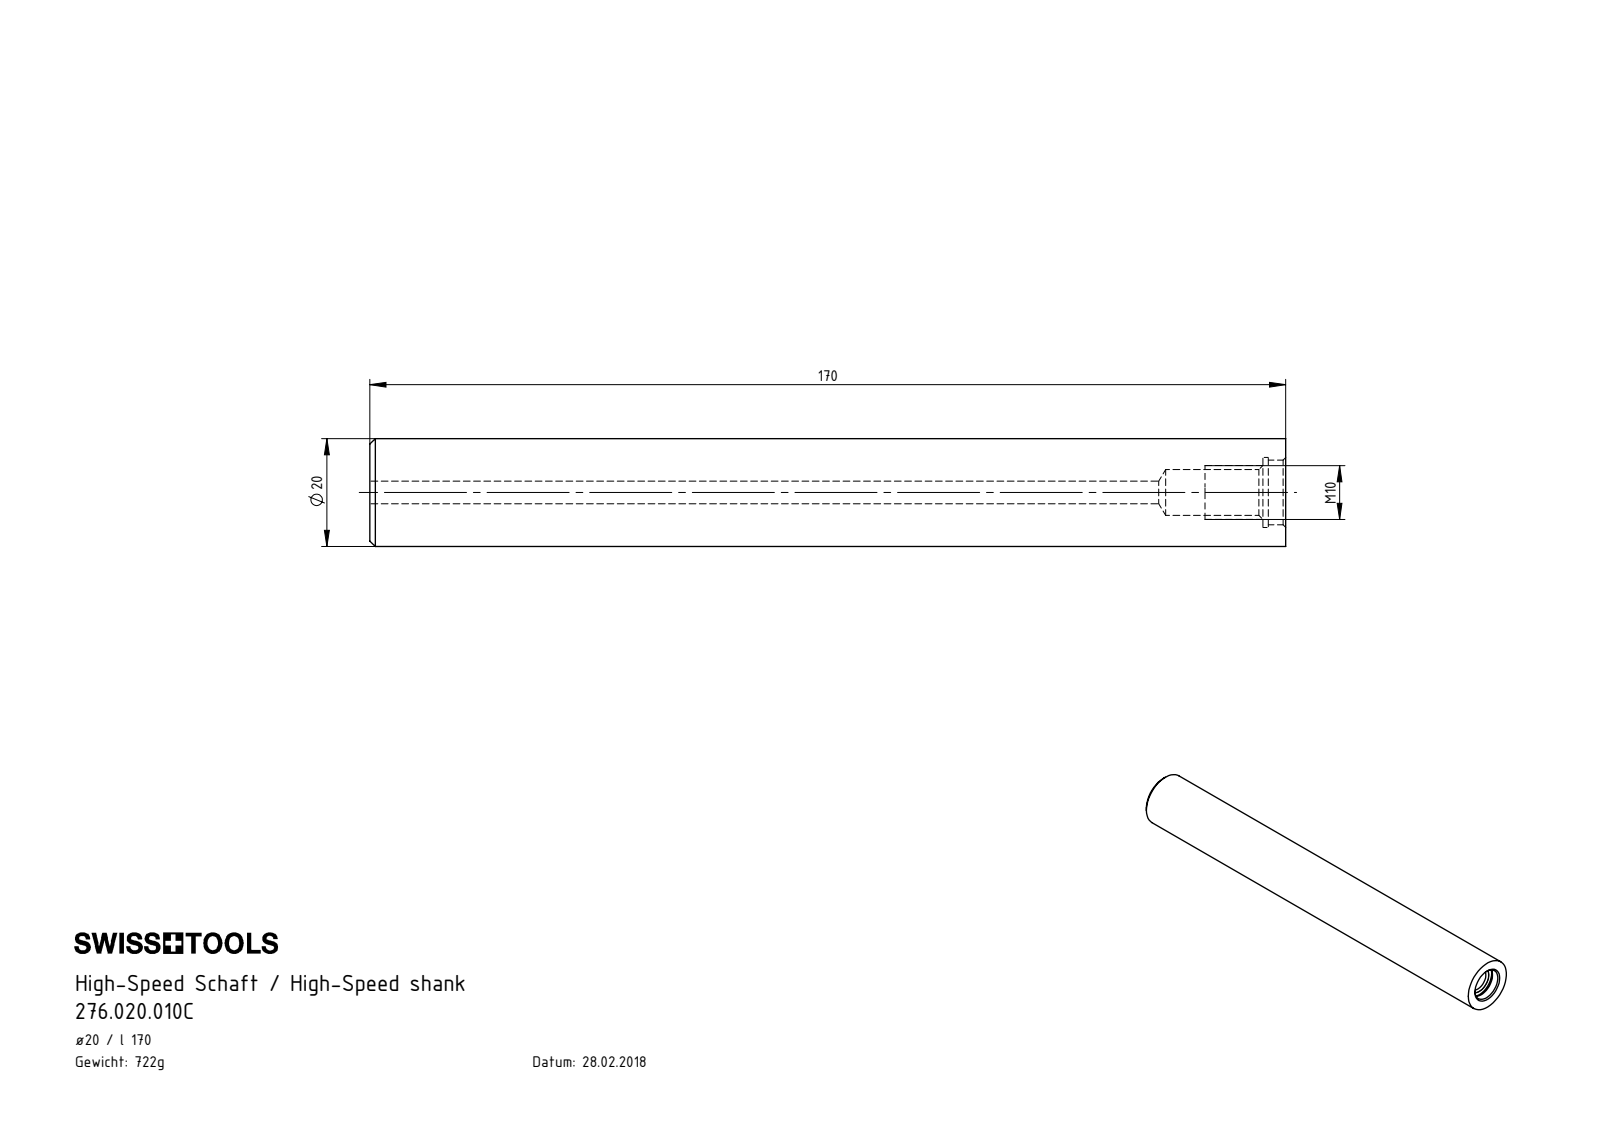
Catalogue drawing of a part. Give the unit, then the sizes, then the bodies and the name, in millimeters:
Units: millimetres
Overall size (bounding box): 170 × 20 × 20
Round holes (diameter × count): ⌀4.2 ×1, ⌀8.5 ×1, ⌀12 ×1, ⌀13 ×1
Round bosses / shafts (diameter × count): ⌀20 ×1
Main face-to-face distances: 170, 165.75, 4.25, 166.75, 1, 3.25
Volume: 49 768 mm³ · Surface area: 13 846 mm²
Bodies: 1 solid, 22 faces (4 planar, 10 cylindrical, 8 other)
Part name (STEP PRODUCT): 276.020.010C
STEP written by: SolidWorks 2017 (CONFIG_CONTROL_DESIGN)
